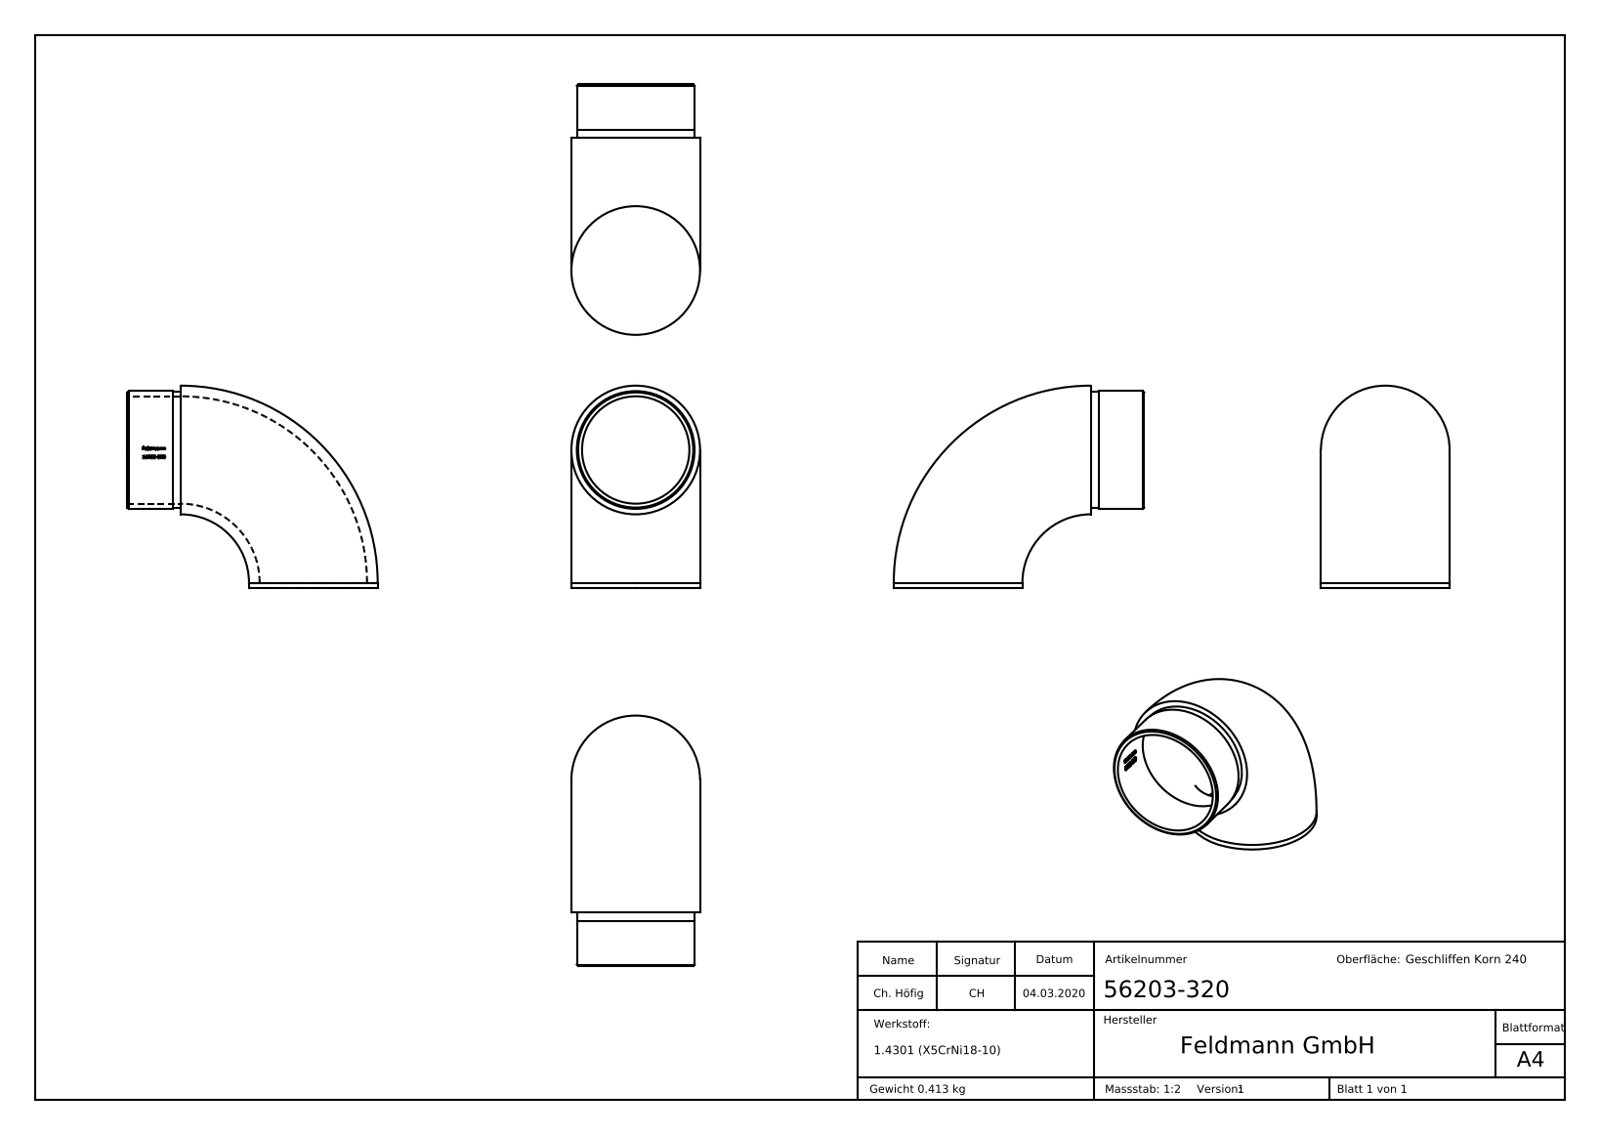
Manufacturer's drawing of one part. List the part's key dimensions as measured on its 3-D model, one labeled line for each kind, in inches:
Part name (STEP PRODUCT): 56203-320
STEP written by: SolidWorks 2015 (CONFIG_CONTROL_DESIGN)
Units: inches
Bodies: 1 solid, 243 faces (90 planar, 27 cylindrical, 126 other)
Overall size (bounding box): 3.701 × 2.992 × 1.902
Volume: 3.193 in³ · Surface area: 48.19 in²
Round holes (diameter × count): ⌀1.587 ×1
Round bosses / shafts (diameter × count): ⌀1.902 ×1, ⌀1.74 ×1, ⌀1.724 ×1
Partial cylindrical surfaces — rounded edges, fillets, slot ends (radius × count): R0.797 ×1
Main face-to-face distances: 0.079, 0.787, 0.118, 0.669, 0.117, 0.015, 0.044, 0.144, 0.129, 0.052
